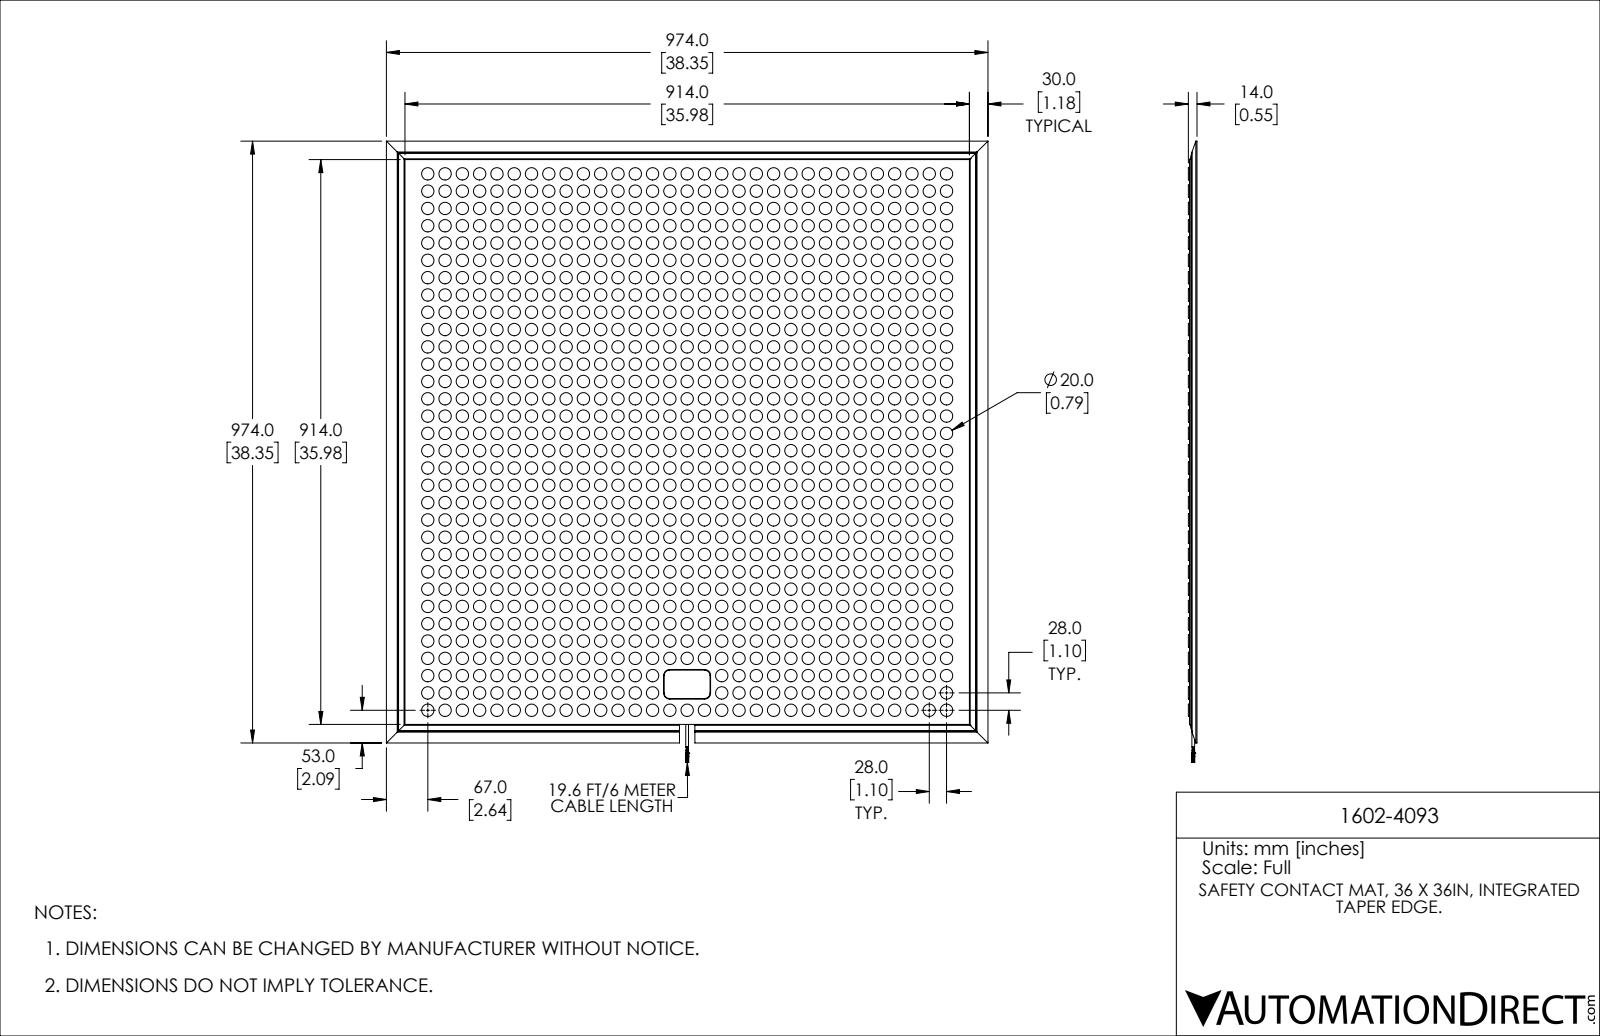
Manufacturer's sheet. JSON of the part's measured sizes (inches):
{"part_name": "1602-4093", "step_written_by": "SolidWorks 2021 (AUTOMOTIVE_DESIGN)", "units": "inches", "bodies": {"solids": 991, "faces": 4145, "planar": 2050, "cylindrical": 2054, "other": 41}, "overall_size": [39.587, 38.346, 0.551], "volume_in3": 686.9, "surface_area_in2": 4271, "round_bosses_or_shafts": [[0.787, 986], [0.047, 20], [0.031, 8], [0.173, 1]], "partial_cylinders_radius": [[0.394, 6], [0.039, 4]], "face_to_face_distances": [0.472, 0.079, 0.551, 35.984, 0.134, 0.055, 0.417, 0.138, 0.059, 0.413]}
